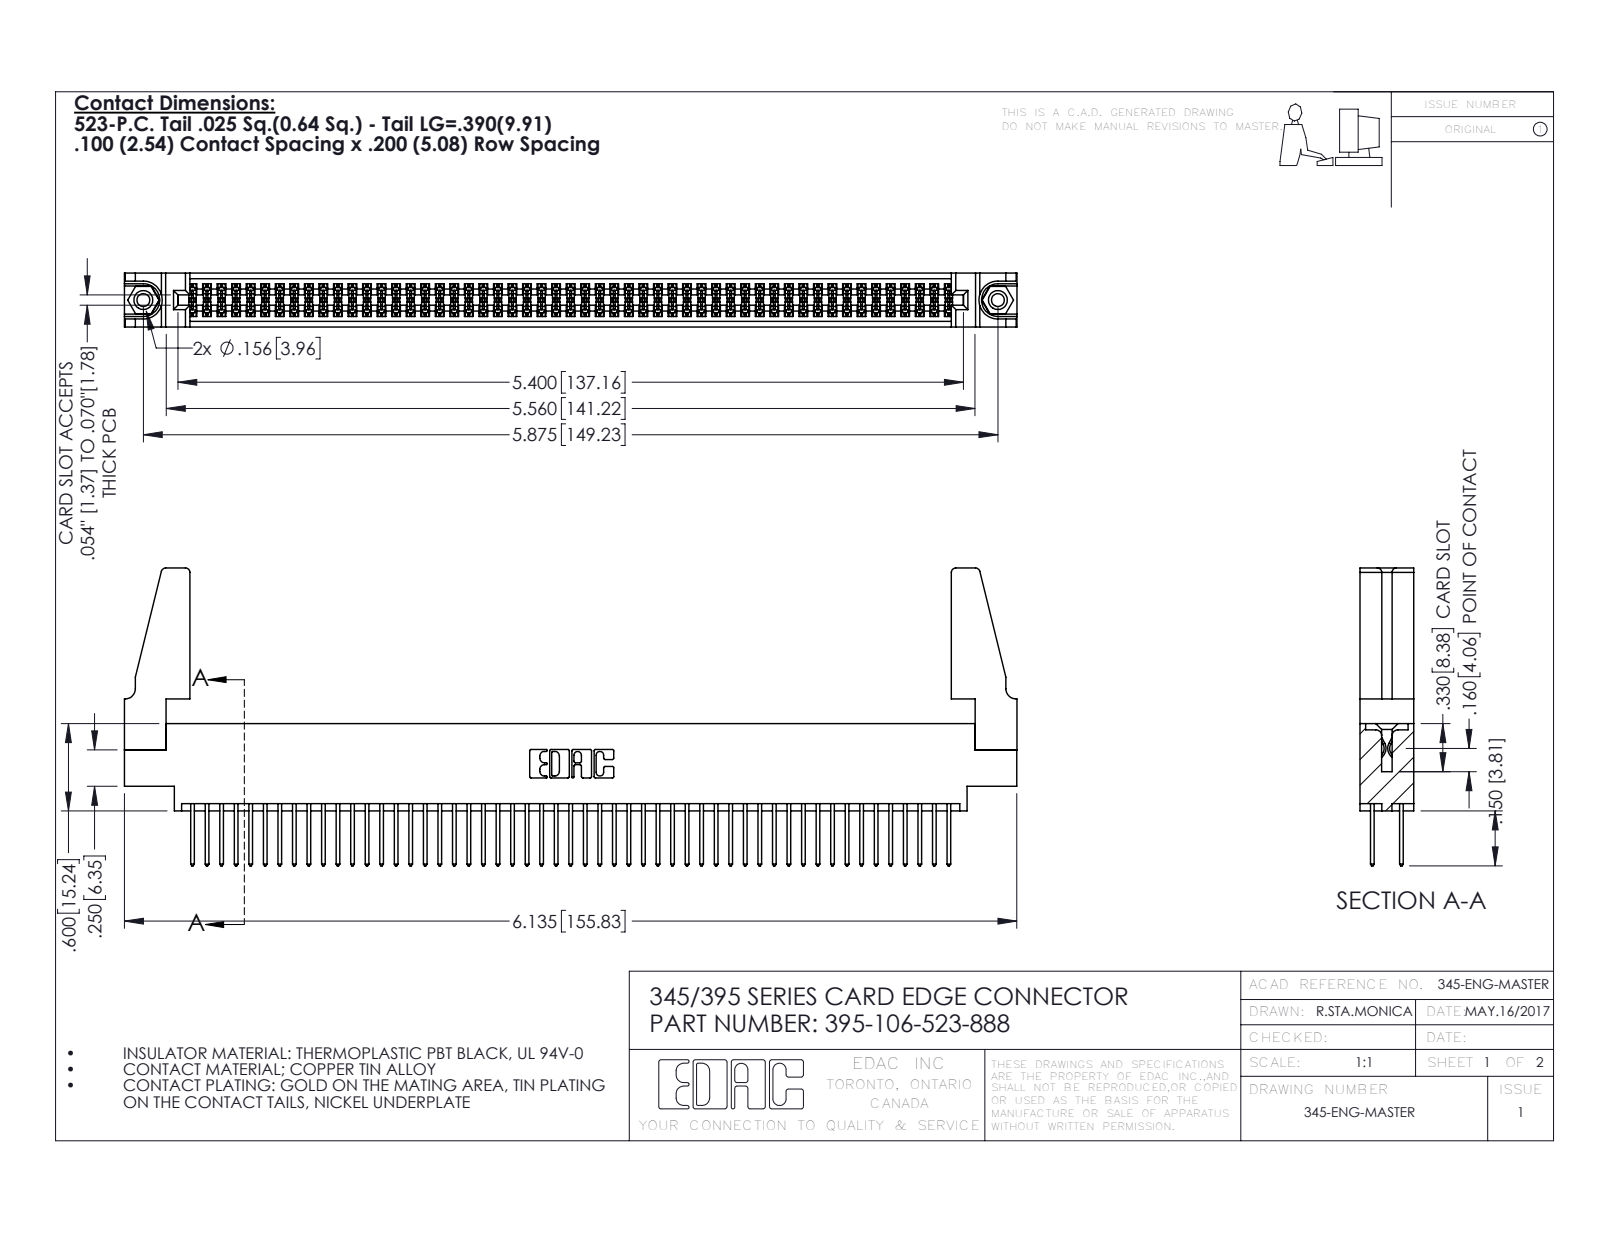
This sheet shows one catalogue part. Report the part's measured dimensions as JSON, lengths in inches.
{"part_name": "345-292-001_345-293-123; 345-220-078_345-220-088; 395-106-523-888; 345-250-001_345-250-001-102 (+1 more)", "step_written_by": "SolidWorks 2016 (CONFIG_CONTROL_DESIGN)", "units": "inches", "bodies": {"solids": 111, "faces": 5554, "planar": 3654, "cylindrical": 1884, "other": 16}, "overall_size": [6.136, 2.047, 0.37], "volume_in3": 1.135, "surface_area_in2": 42.06, "round_holes": [[0.089, 2], [0.125, 2], [0.156, 2], [0.064, 1]], "round_bosses_or_shafts": [[0.155, 2]], "partial_cylinders_radius": [[0.006, 159], [0.01, 106], [0.01, 22], [0.03, 8], [0.007, 6], [0.031, 6], [0.026, 3], [0.014, 2]], "face_to_face_distances": [0.072, 0.298, 0.37, 0.2, 0.098, 0.272, 0.025, 0.225, 0.175, 0.149], "hole_center_spacings": [0.27, 5.639, 5.875]}
